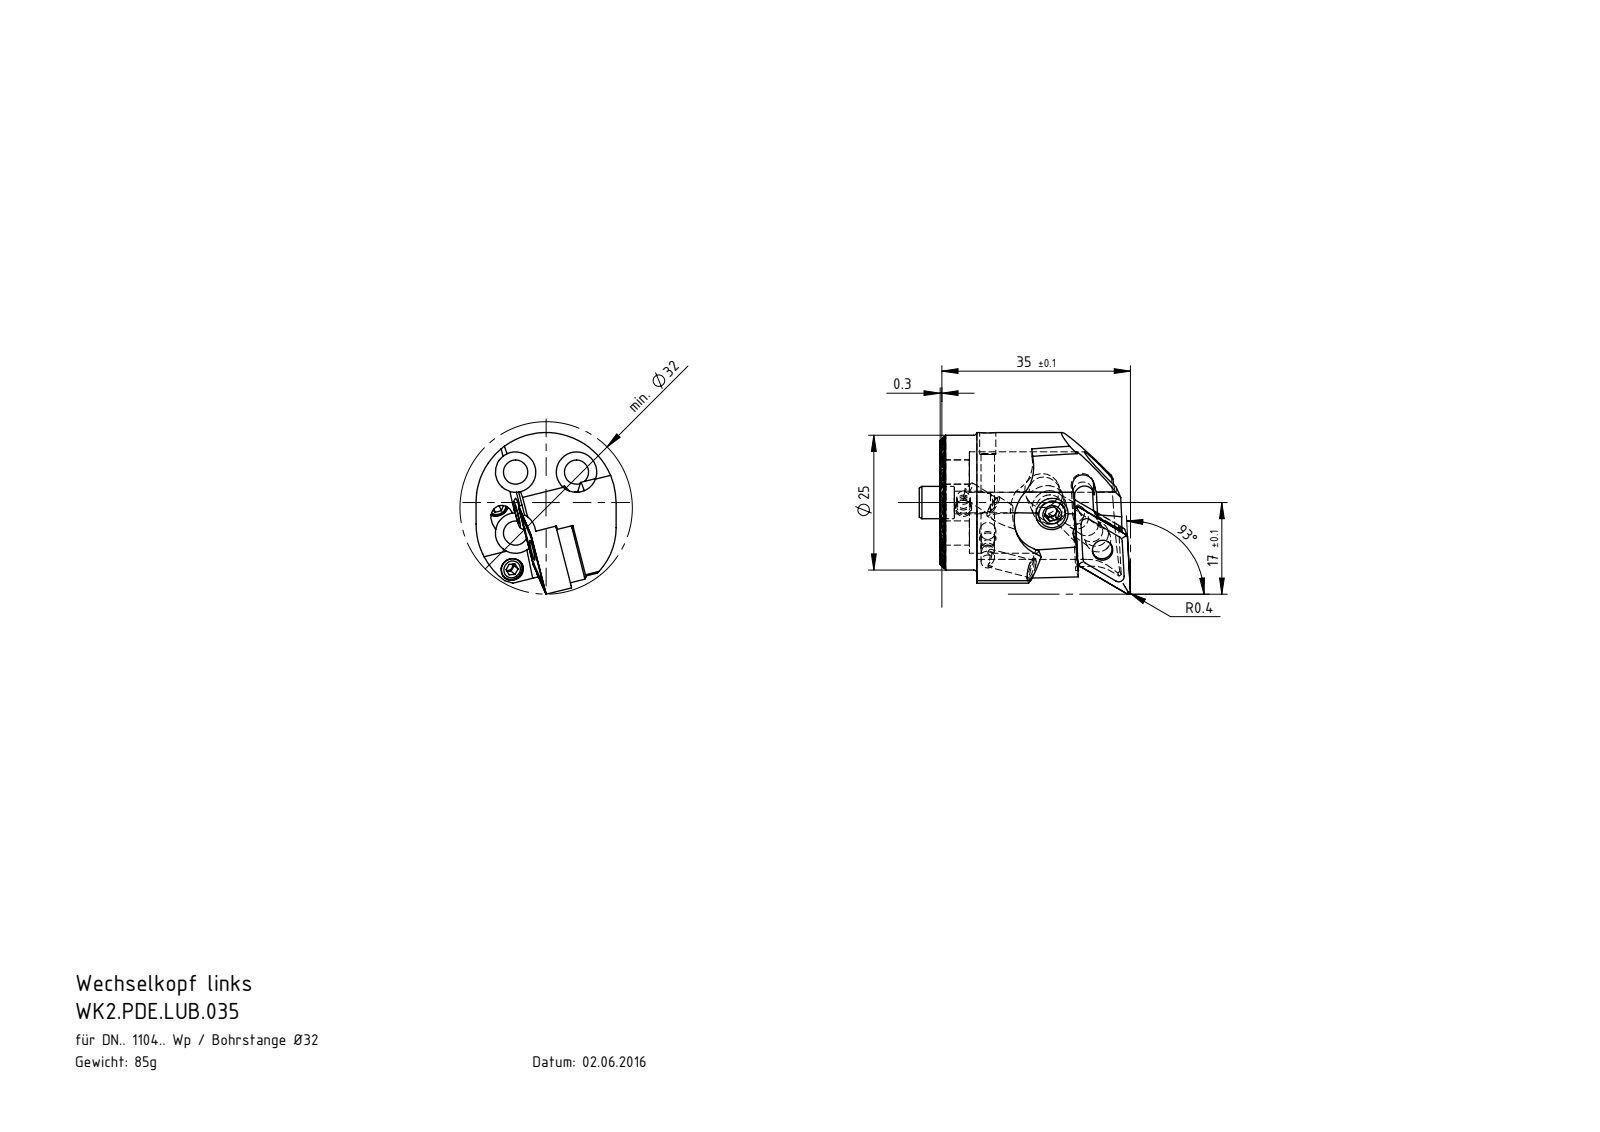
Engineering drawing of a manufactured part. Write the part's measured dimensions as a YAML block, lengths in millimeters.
part_name: "WDE-ER4.101.017_A; WK2-PDE.LUB.035_A; KVT_MB_600_030; WK2-ER1.001.012_A_Fertigbearbeitung (+6 more)"
step_written_by: "SolidWorks 2017 (AUTOMOTIVE_DESIGN)"
units: millimeters
bodies: {solids: 15, faces: 476, planar: 255, cylindrical: 111, other: 110}
overall_size: [39.21, 38.5, 33]
volume: 17755
surface_area: 10240
round_holes:
  - {diameter: 2.38, count: 3}
  - {diameter: 2.5, count: 3}
  - {diameter: 4.2, count: 3}
  - {diameter: 5.5, count: 3}
  - {diameter: 9, count: 3}
  - {diameter: 1.7, count: 2}
  - {diameter: 3, count: 2}
  - {diameter: 3.3, count: 2}
  - {diameter: 3.81, count: 1}
  - {diameter: 4.8, count: 1}
  - {diameter: 5, count: 1}
  - {diameter: 6.4, count: 1}
round_bosses_or_shafts:
  - {diameter: 3, count: 3}
  - {diameter: 6, count: 2}
  - {diameter: 4, count: 2}
  - {diameter: 32, count: 1}
  - {diameter: 5.9, count: 1}
  - {diameter: 2.87, count: 1}
partial_cylinders:
  - {radius: 0.12, count: 22}
  - {radius: 0.4, count: 8}
  - {radius: 2.1, count: 5}
  - {radius: 7, count: 2}
  - {radius: 1.83, count: 1}
  - {radius: 1.85, count: 1}
  - {radius: 2.25, count: 1}
  - {radius: 2.35, count: 1}
face_to_face_distances: [1.3, 2.6, 3.9, 5.2, 7.8, 6.5, 12.99, 11.69, 14.29, 10.39]
hole_center_spacings: [11, 15.56, 11.8, 22.01]
